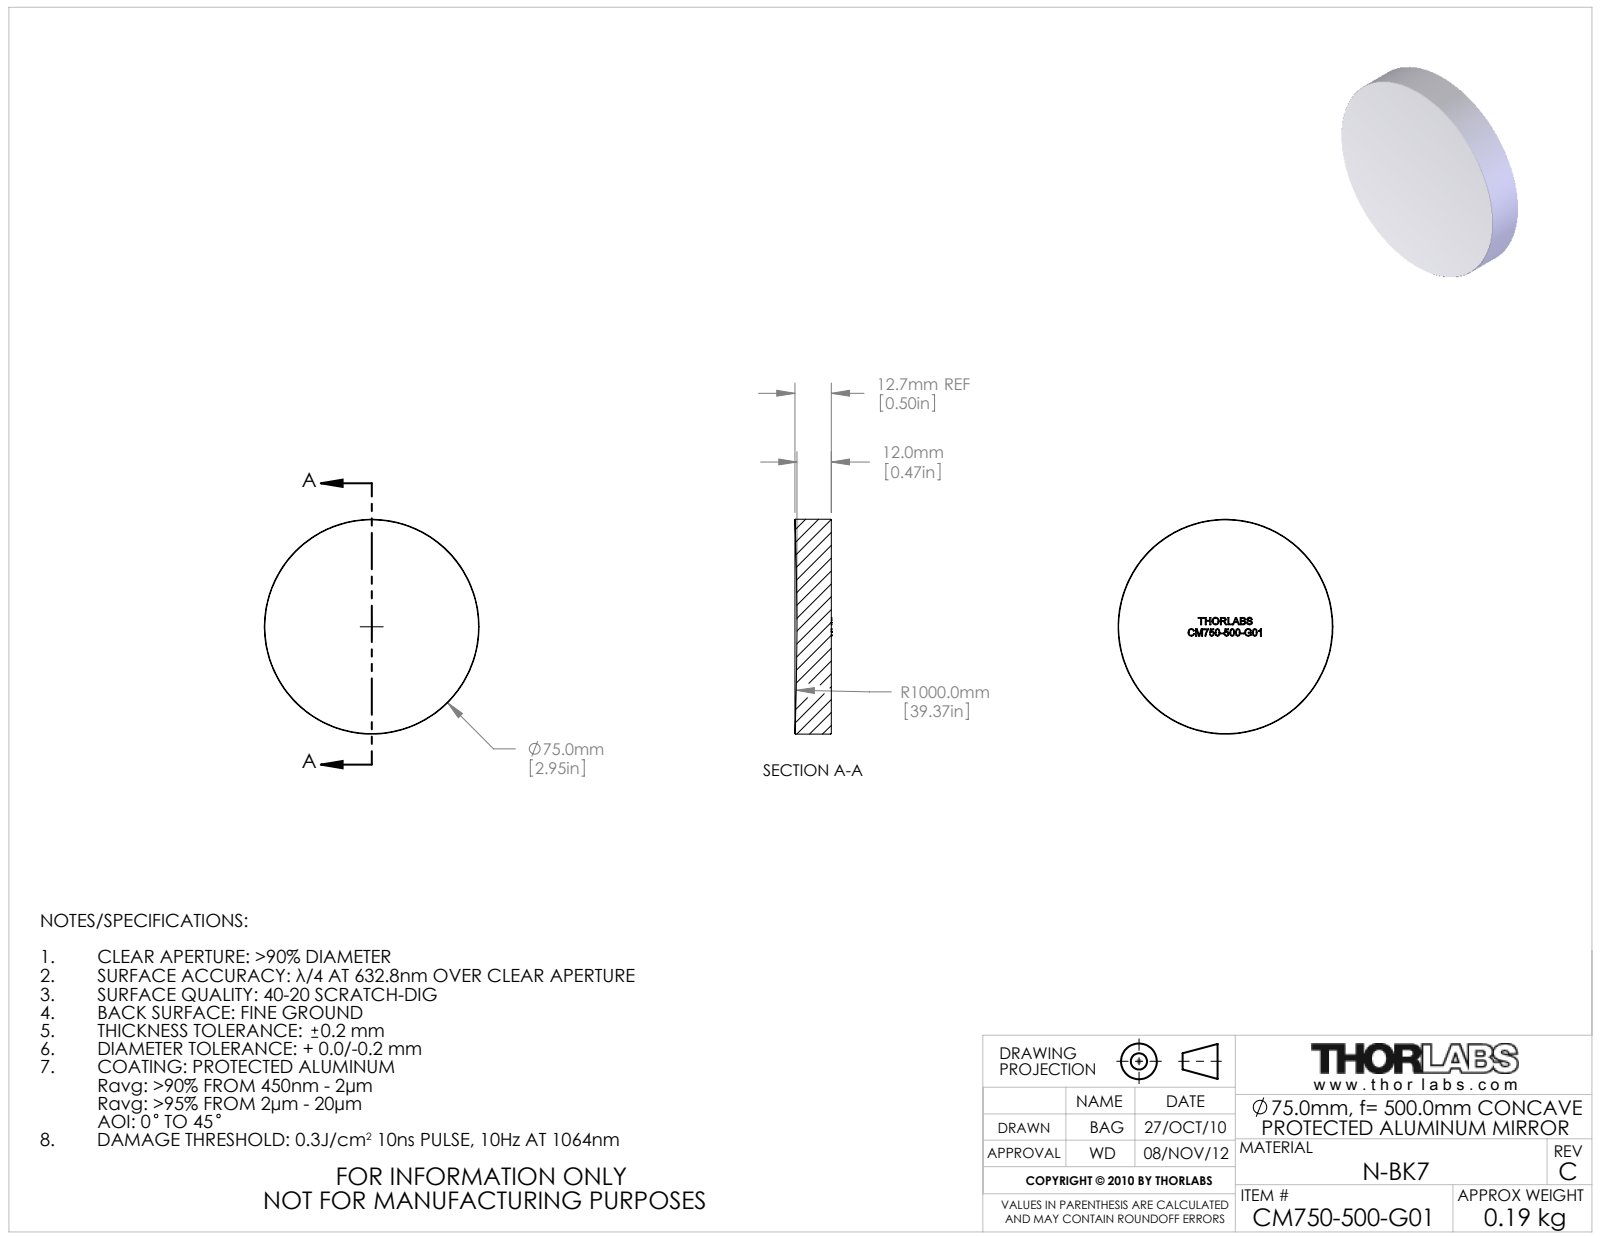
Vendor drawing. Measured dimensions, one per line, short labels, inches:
name: 12020-E0W
written by: SolidWorks 2009 (AUTOMOTIVE_DESIGN)
unit: in
bodies: 1 solid, 275 faces (143 planar, 2 cylindrical, 130 other)
size: 2.953 × 2.953 × 0.5
volume: 3.329 in³; area: 18.25 in²
bosses: 1× ⌀2.953
face distances: 0.014, 0.101, 0.015, 0.258, 0.145, 0.146, 0.097, 0.013, 0.111, 0.126
